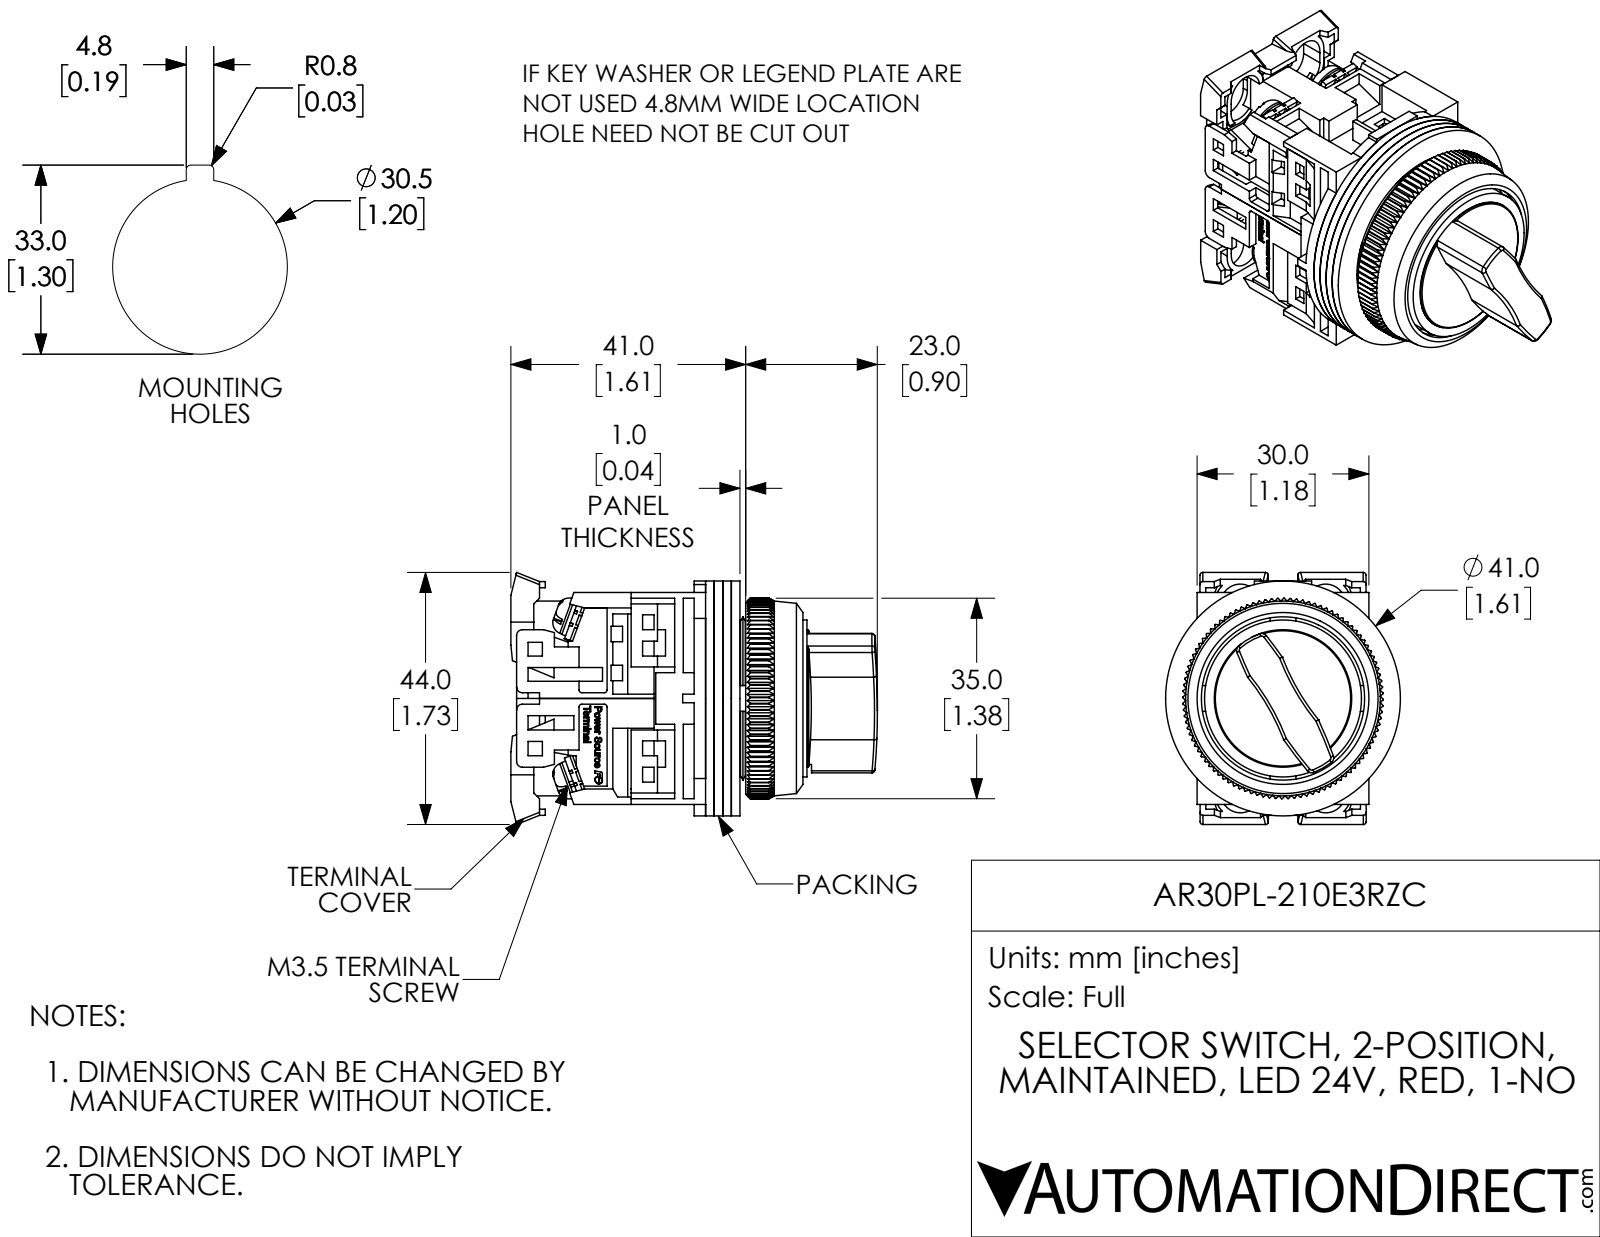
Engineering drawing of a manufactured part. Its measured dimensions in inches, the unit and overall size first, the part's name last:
Units: inches
Overall size (bounding box): 2.52 × 1.732 × 1.614
Round holes (diameter × count): ⌀0.138 ×8, ⌀0.142 ×4, ⌀0.118 ×1, ⌀0.472 ×1, ⌀0.709 ×1, ⌀0.768 ×1, ⌀0.827 ×1, ⌀1.122 ×1, ⌀1.181 ×1, ⌀1.252 ×1
Round bosses / shafts (diameter × count): ⌀0.26 ×4, ⌀0.138 ×4, ⌀0.063 ×2, ⌀1.614 ×1, ⌀1.15 ×1, ⌀1.079 ×1, ⌀0.945 ×1, ⌀0.886 ×1
Partial cylindrical surfaces — rounded edges, fillets, slot ends (radius × count): R0.059 ×16, R0.02 ×12, R0.039 ×8, R0.138 ×4, R0.177 ×4, R0.118 ×2, R1.575 ×2, R2.953 ×2
Main face-to-face distances: 0.059, 0.118, 0.177, 0.039, 0.079, 1.417, 1.358, 0.811, 0.197, 0.02
Hole centre spacings: 0.579, 0.61
Volume: 2.238 in³ · Surface area: 59.31 in²
Bodies: 25 solids, 2434 faces (1731 planar, 305 cylindrical, 398 other)
Part name (STEP PRODUCT): AR30PL-210E3RZC
STEP written by: SolidWorks 2017 (AUTOMOTIVE_DESIGN)
